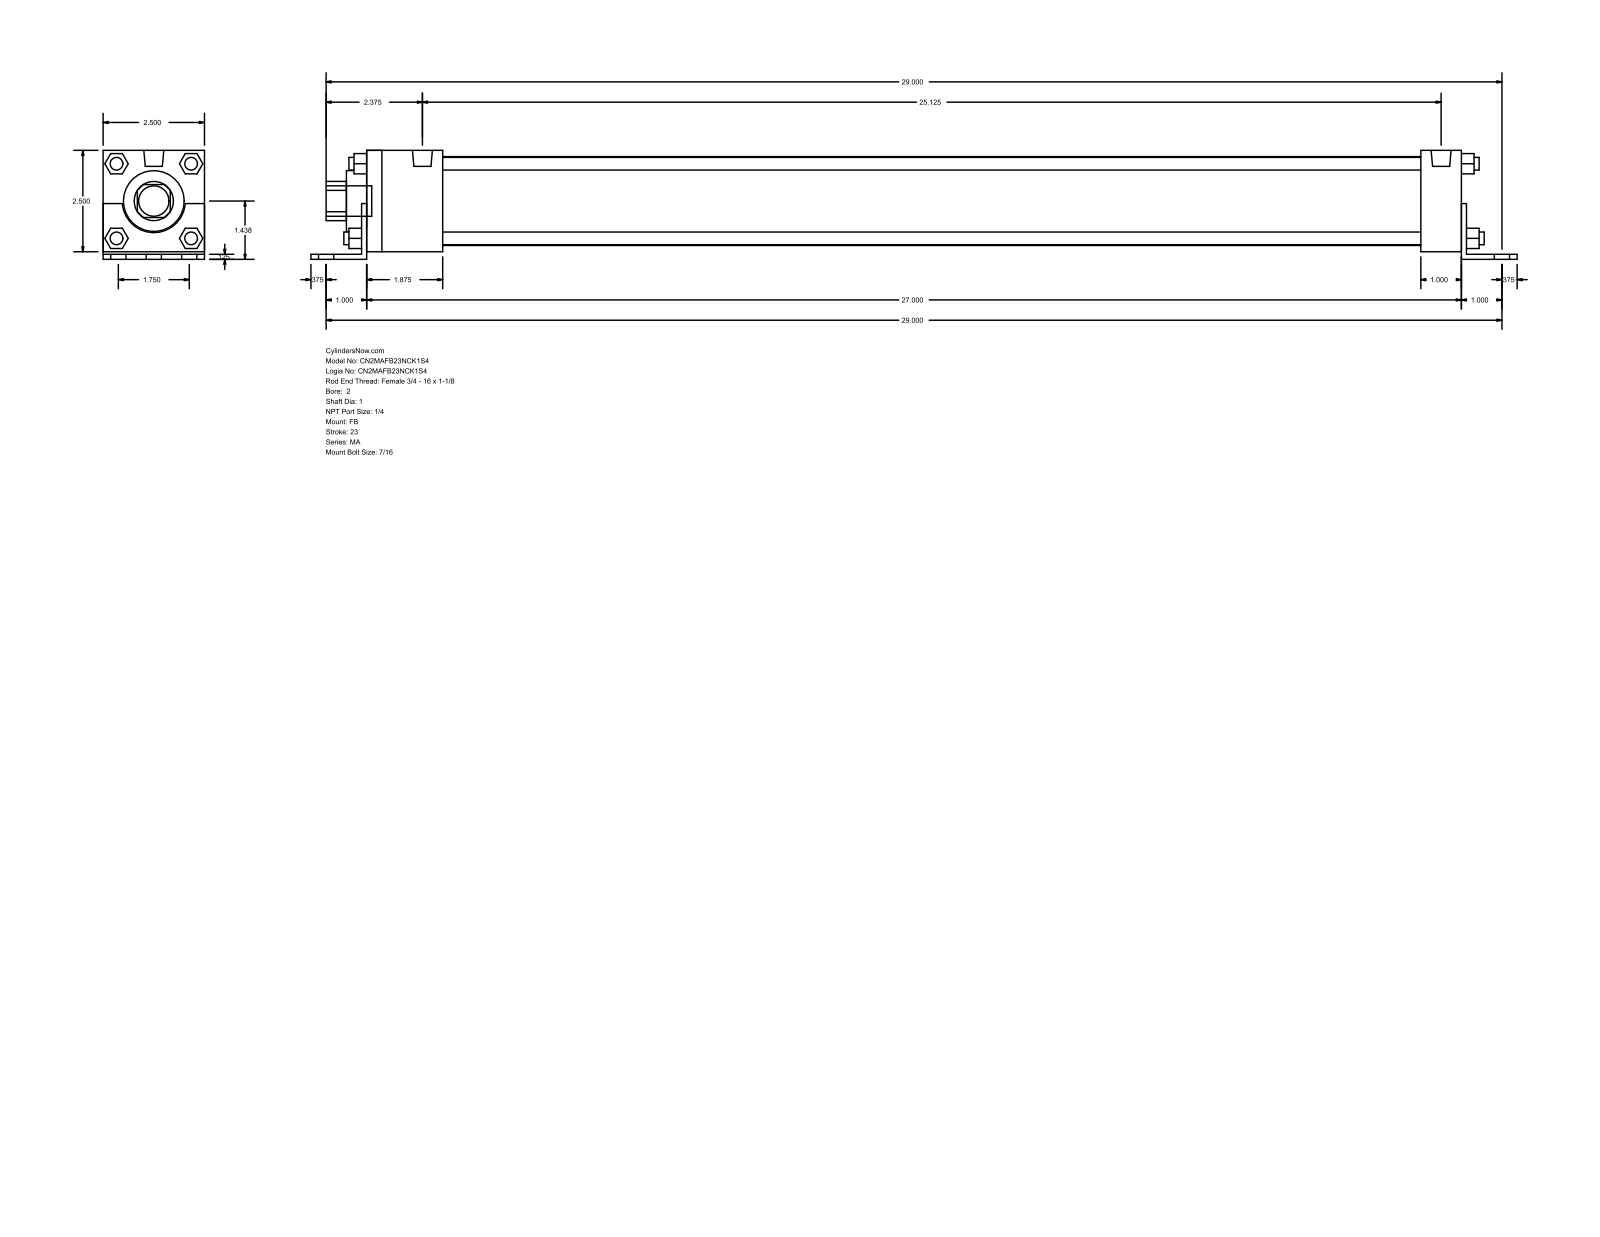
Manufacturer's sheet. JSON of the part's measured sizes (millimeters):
{"part_name": "MA_FB__0200_1", "step_written_by": "GSSL Pune (CONFIG_CONTROL_DESIGN)", "units": "millimeters", "bodies": {"solids": 0, "faces": 140, "planar": 105, "cylindrical": 35, "other": 0}, "overall_size": [755.65, 68.26, 63.5], "round_holes": [[25.4, 1], [38.1, 1], [55.63, 1]], "round_bosses_or_shafts": [[7.94, 8], [11.11, 6], [12.49, 2], [19.05, 1]], "partial_cylinders_radius": [[12.29, 1], [19.81, 1]], "face_to_face_distances": [63.5, 3.17, 4.76, 68.26, 1.59, 65.09, 12.7, 3.18, 685.8, 688.98]}
